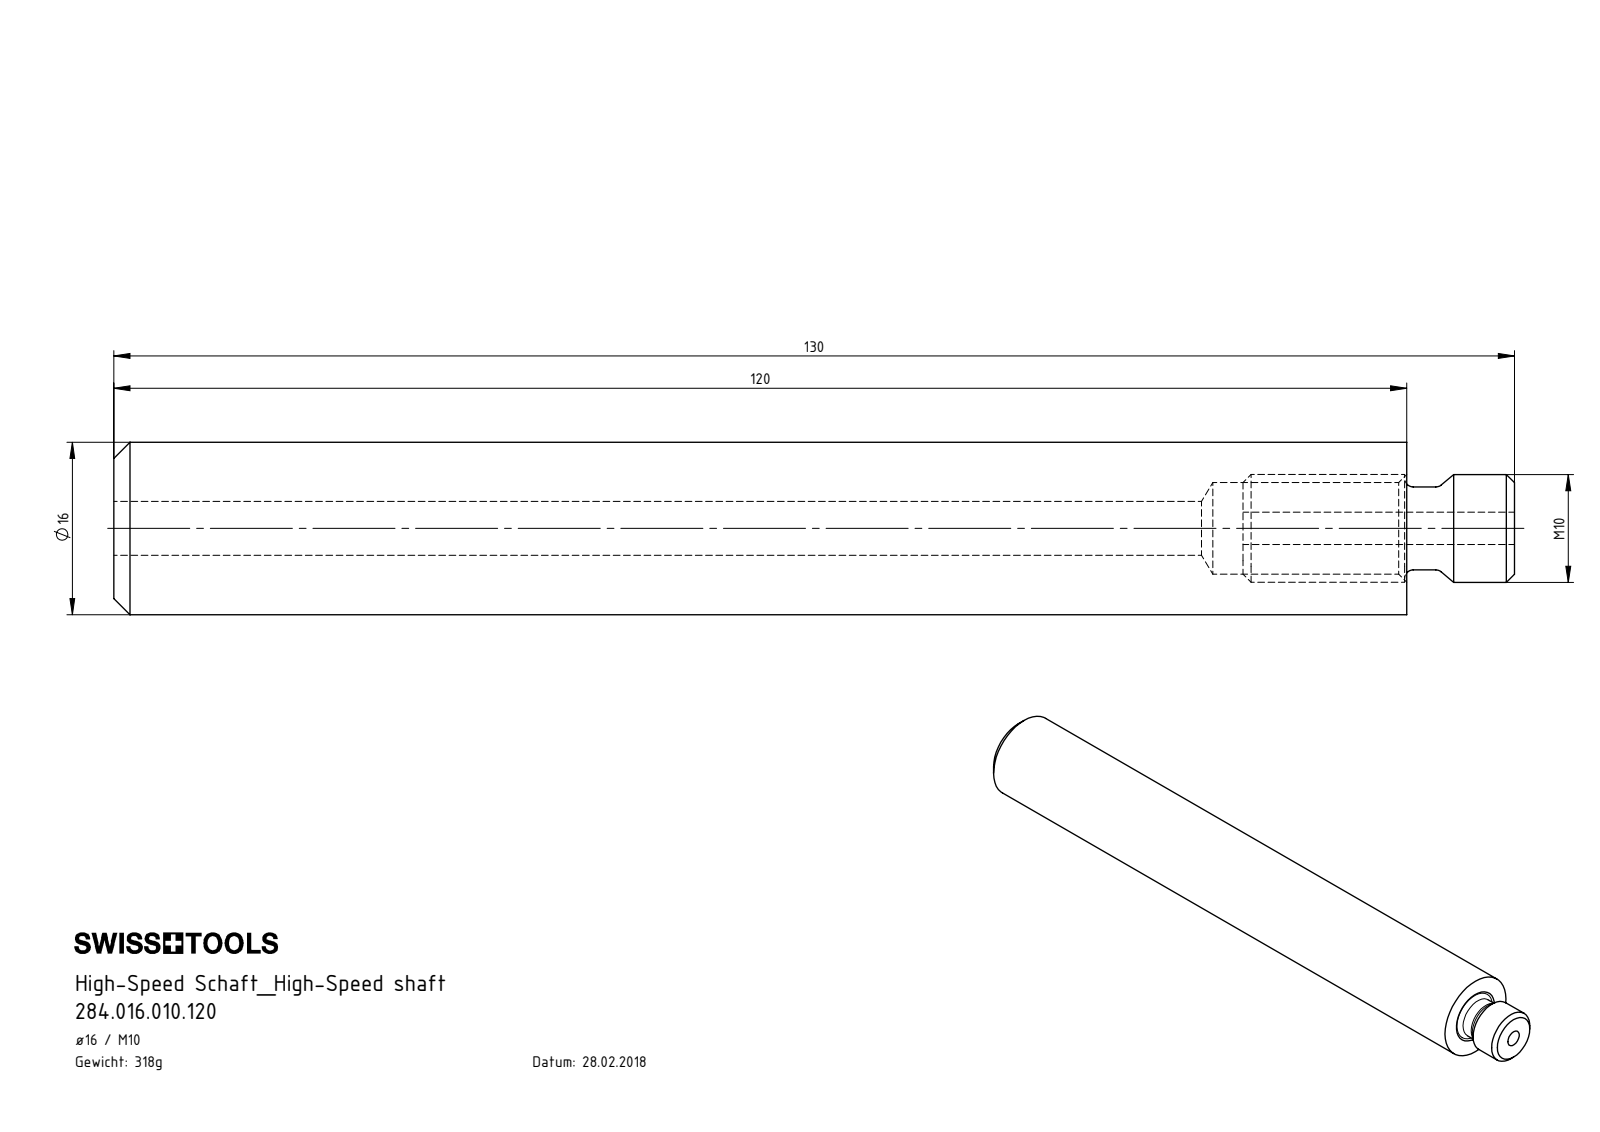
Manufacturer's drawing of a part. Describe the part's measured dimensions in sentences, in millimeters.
The part is named "HM1-BG1.010.025_A; U16-HS0.K01.120; HM1-U16.001.120_A". Its 3-D file was written by "SolidWorks 2017 (CONFIG_CONTROL_DESIGN)". It is 2 solids with 35 faces: 5 planar, 14 cylindrical and 16 other. Overall it measures 130 by 16 by 16 millimeters. Its volume is 22 687 cubic millimeters and its surface area 9 559 square millimeters. Round holes: 1 of diameter 3, 1 of diameter 5, 1 of diameter 8.5. Round bosses or shafts: 1 of diameter 16, 1 of diameter 10, 1 of diameter 7.7. The main face-to-face distances are 120, 104.8, 130, 15.2, 25.2, 10, 119.8, 15, 10.2.
